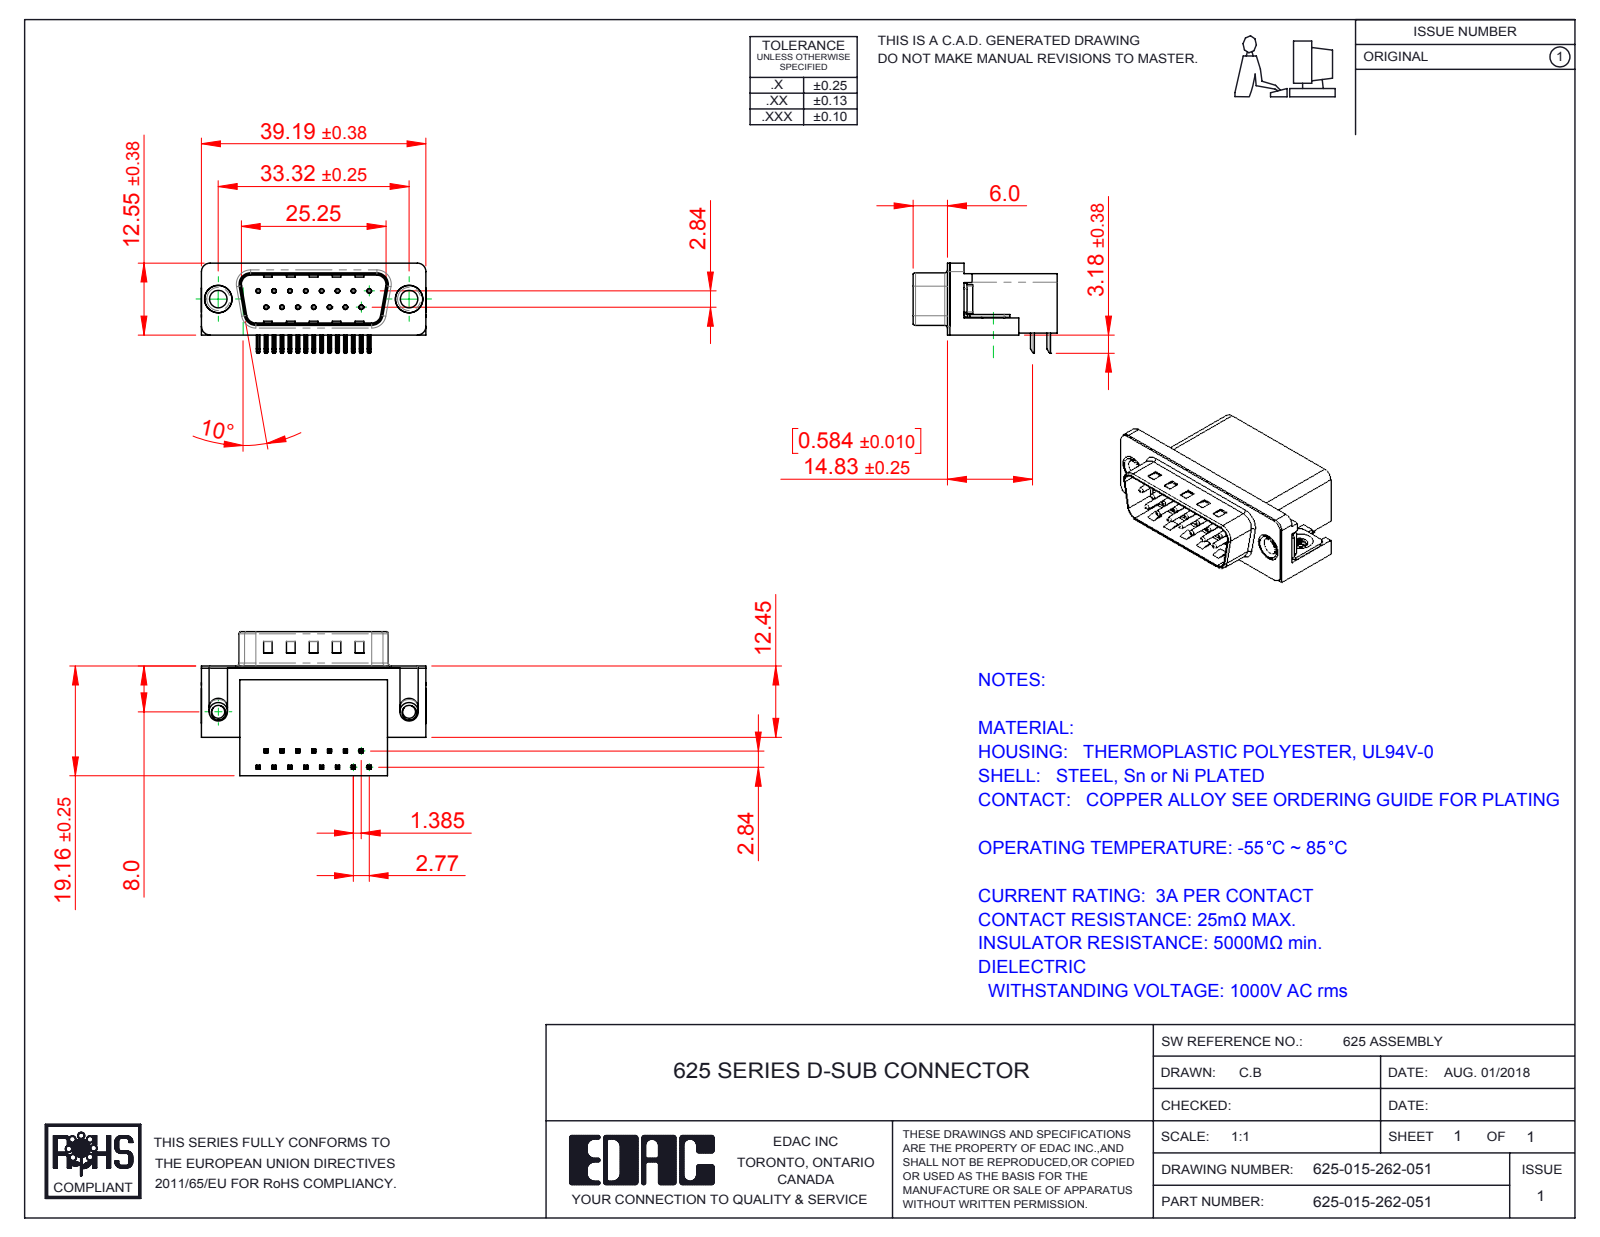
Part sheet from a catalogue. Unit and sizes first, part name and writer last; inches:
Units: inches
Overall size (bounding box): 1.544 × 0.991 × 0.619
Round holes (diameter × count): ⌀0.014 ×15, ⌀0.031 ×15, ⌀0.089 ×2, ⌀0.12 ×2, ⌀0.157 ×2, ⌀0.189 ×2, ⌀0.197 ×2
Round bosses / shafts (diameter × count): ⌀0.03 ×15, ⌀0.193 ×2, ⌀0.187 ×2, ⌀0.152 ×2, ⌀0.128 ×2
Partial cylindrical surfaces — rounded edges, fillets, slot ends (radius × count): R0.01 ×68, R0.005 ×30, R0.039 ×16, R0.02 ×9, R0.063 ×8, R0.059 ×6, R0.035 ×4, R0.079 ×4
Main face-to-face distances: 0.016, 0.407, 0.739, 0.083, 0.754, 0.412, 0.067, 0.428, 0.345, 0.64
Hole centre spacings: 0.124, 0.109, 0.218, 0.327, 0.436, 0.198, 0.198, 0.294
Volume: 0.381 in³ · Surface area: 10.04 in²
Bodies: 21 solids, 1471 faces (895 planar, 441 cylindrical, 135 other)
Part name (STEP PRODUCT): 625 Housing_15 Socket; 625 Thru Hole Rivet; 625 Shell_15 Socket; 625 4-40 Threaded Board Mount (+3 more)
STEP written by: SolidWorks 2016 (CONFIG_CONTROL_DESIGN)
